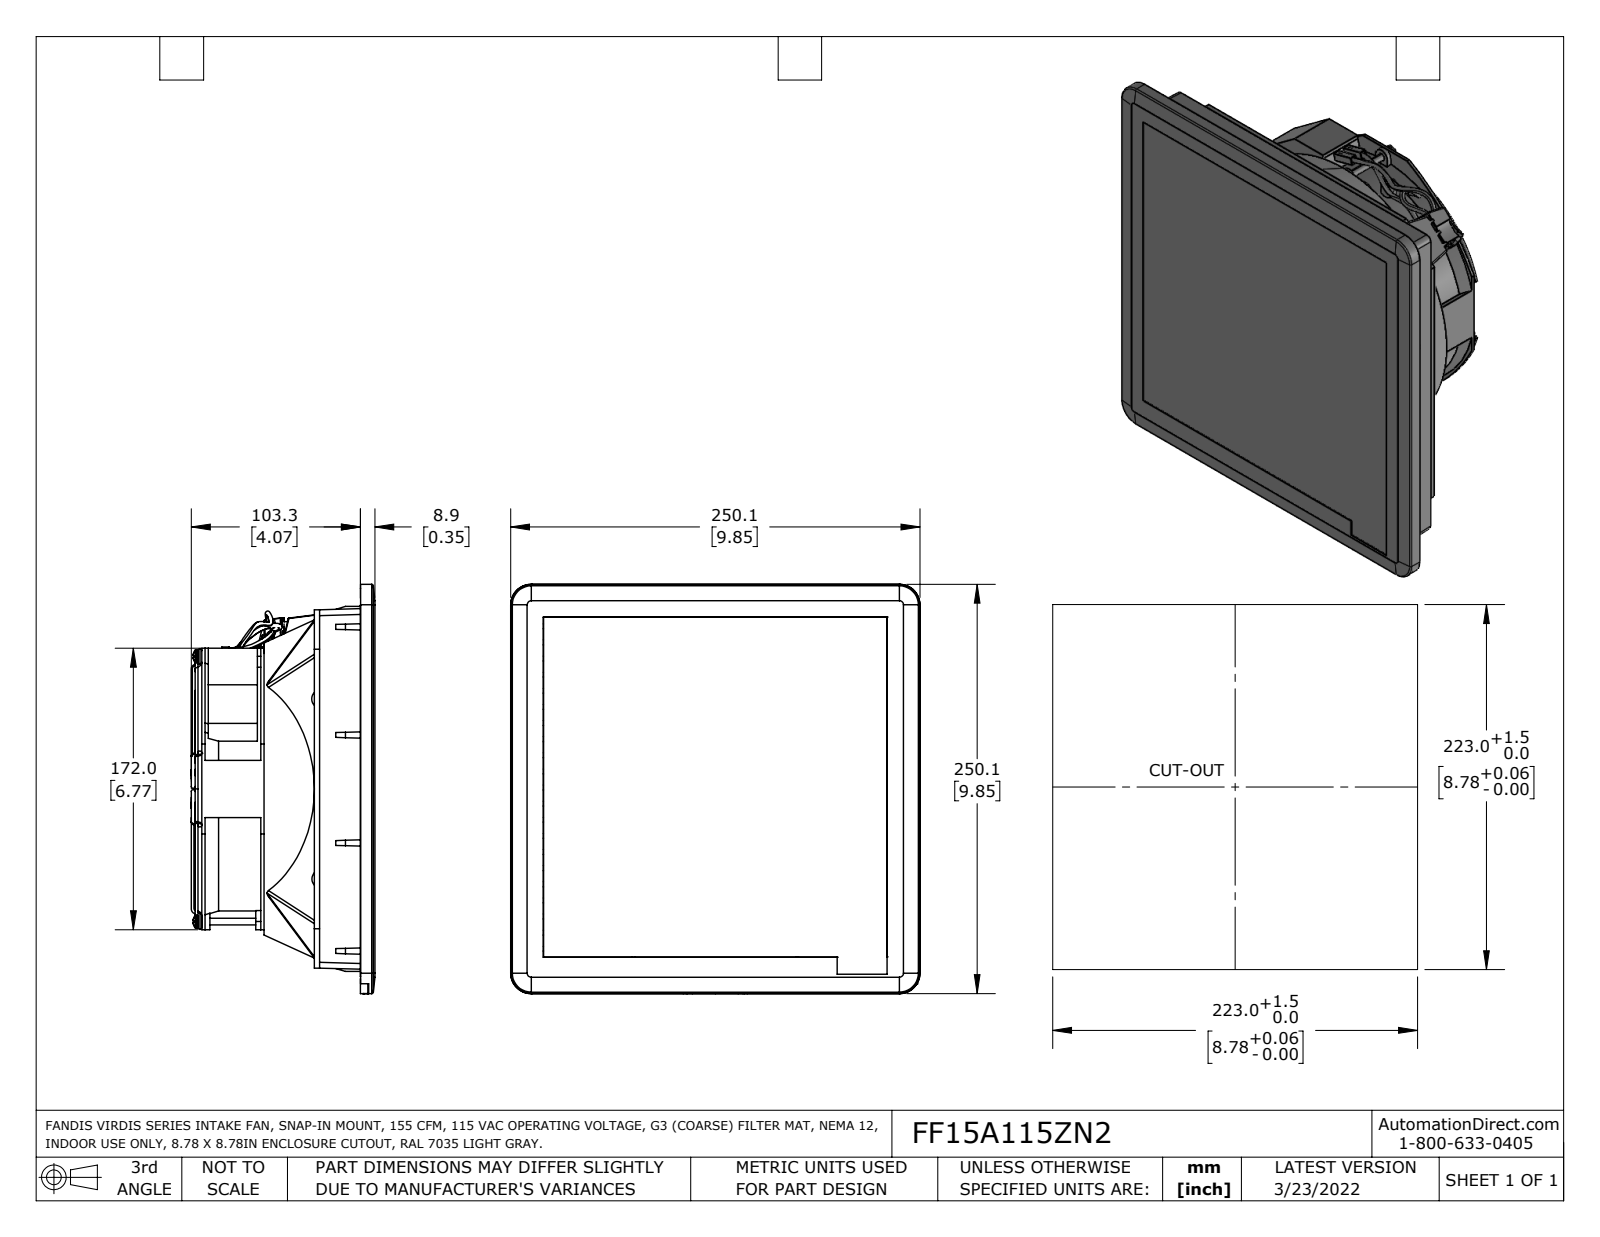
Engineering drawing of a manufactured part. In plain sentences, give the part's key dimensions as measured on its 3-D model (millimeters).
The part is named "FF15AxxxyN2 (p.c.)". Its 3-D file was written by "SolidWorks 2021 (AUTOMOTIVE_DESIGN)". It is 26 solids with 1099 faces: 585 planar, 287 cylindrical and 227 other. Overall it measures 250.1 by 250.1 by 112.2 millimeters. Its volume is 3 595 000 cubic millimeters and its surface area 235 300 square millimeters. Round holes: 2 of diameter 5, 1 of diameter 1, 1 of diameter 3.5, 1 of diameter 4.4. Round bosses or shafts: 2 of diameter 8, 2 of diameter 4, 2 of diameter 3.3, 1 of diameter 149, 1 of diameter 9, 1 of diameter 1. Partial cylindrical surfaces (rounded edges, fillets, slot ends): 33 of radius 0.3, 19 of radius 0.5, 15 of radius 0.4, 13 of radius 1, 11 of radius 0.7, 10 of radius 5, 8 of radius 0.8, 8 of radius 1.3. The main face-to-face distances are 105.3, 8.4, 96.9, 0.5, 8.9, 105.8, 2, 36.5, 36, 34. The hole center spacings are 16.4, 162, 163.6.
